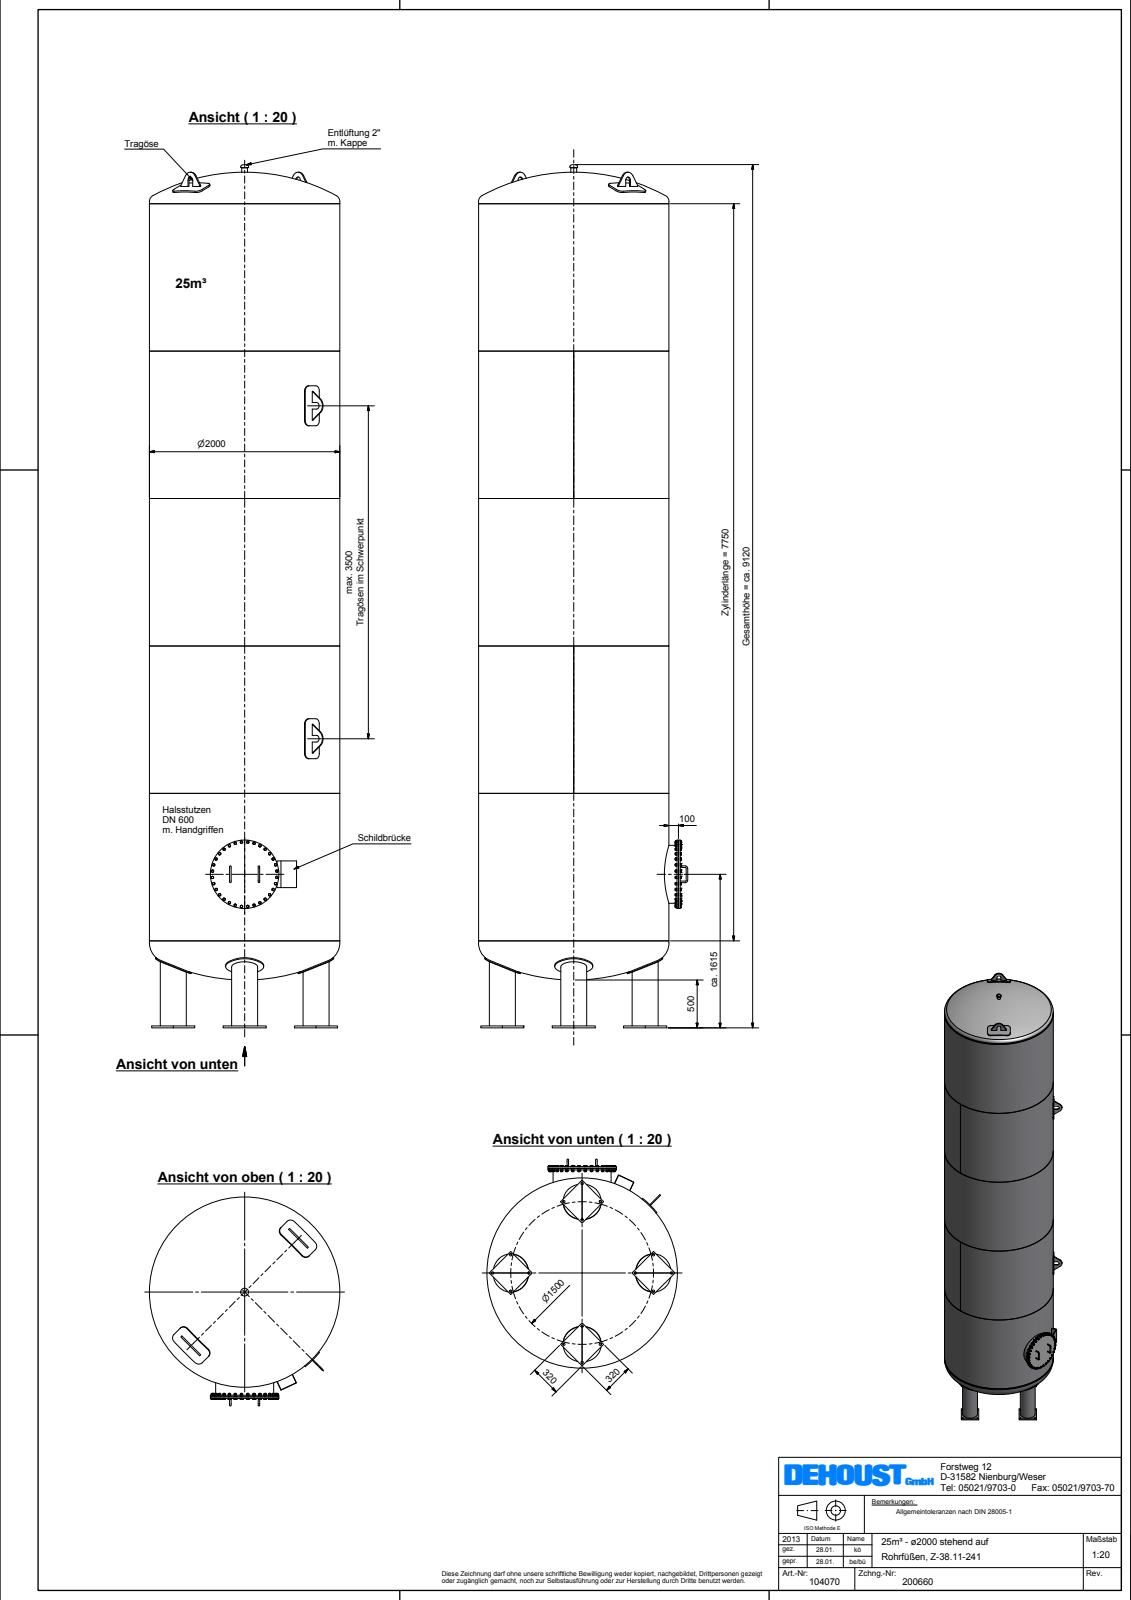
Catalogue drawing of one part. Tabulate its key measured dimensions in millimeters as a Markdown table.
| quantity | value |
| --- | --- |
| part name | Beh\\S\\dlter_Z-38_11-241_2000_025_KV |
| STEP written by | Autodesk Inventor 2012 (AUTOMOTIVE_DESIGN) |
| units | millimeters |
| bodies | 7 solids, 1122 faces (636 planar, 164 cylindrical, 322 other) |
| overall size | 9075.43 × 2197 × 2000 |
| volume | 1 233 000 000 mm³ |
| surface area | 120 000 000 mm² |
| round holes (diameter × count) | 257 × 4, 598 × 1, 1988 × 1 |
| round bosses / shafts (diameter × count) | 16 × 38, 22.5 × 32, 400 × 4, 273 × 4, 2000 × 1, 720 × 1, 660 × 1, 610 × 1 |
| partial cylindrical surfaces (radius × count) | 56 × 16, 35 × 4, 85 × 4, 1010 × 1 |
| main face-to-face distances | 914.59, 20, 35, 894.59, 16, 19, 10, 3, 2.95, 176.98 |
| hole center spacings | 750, 1060.66, 1500 |
